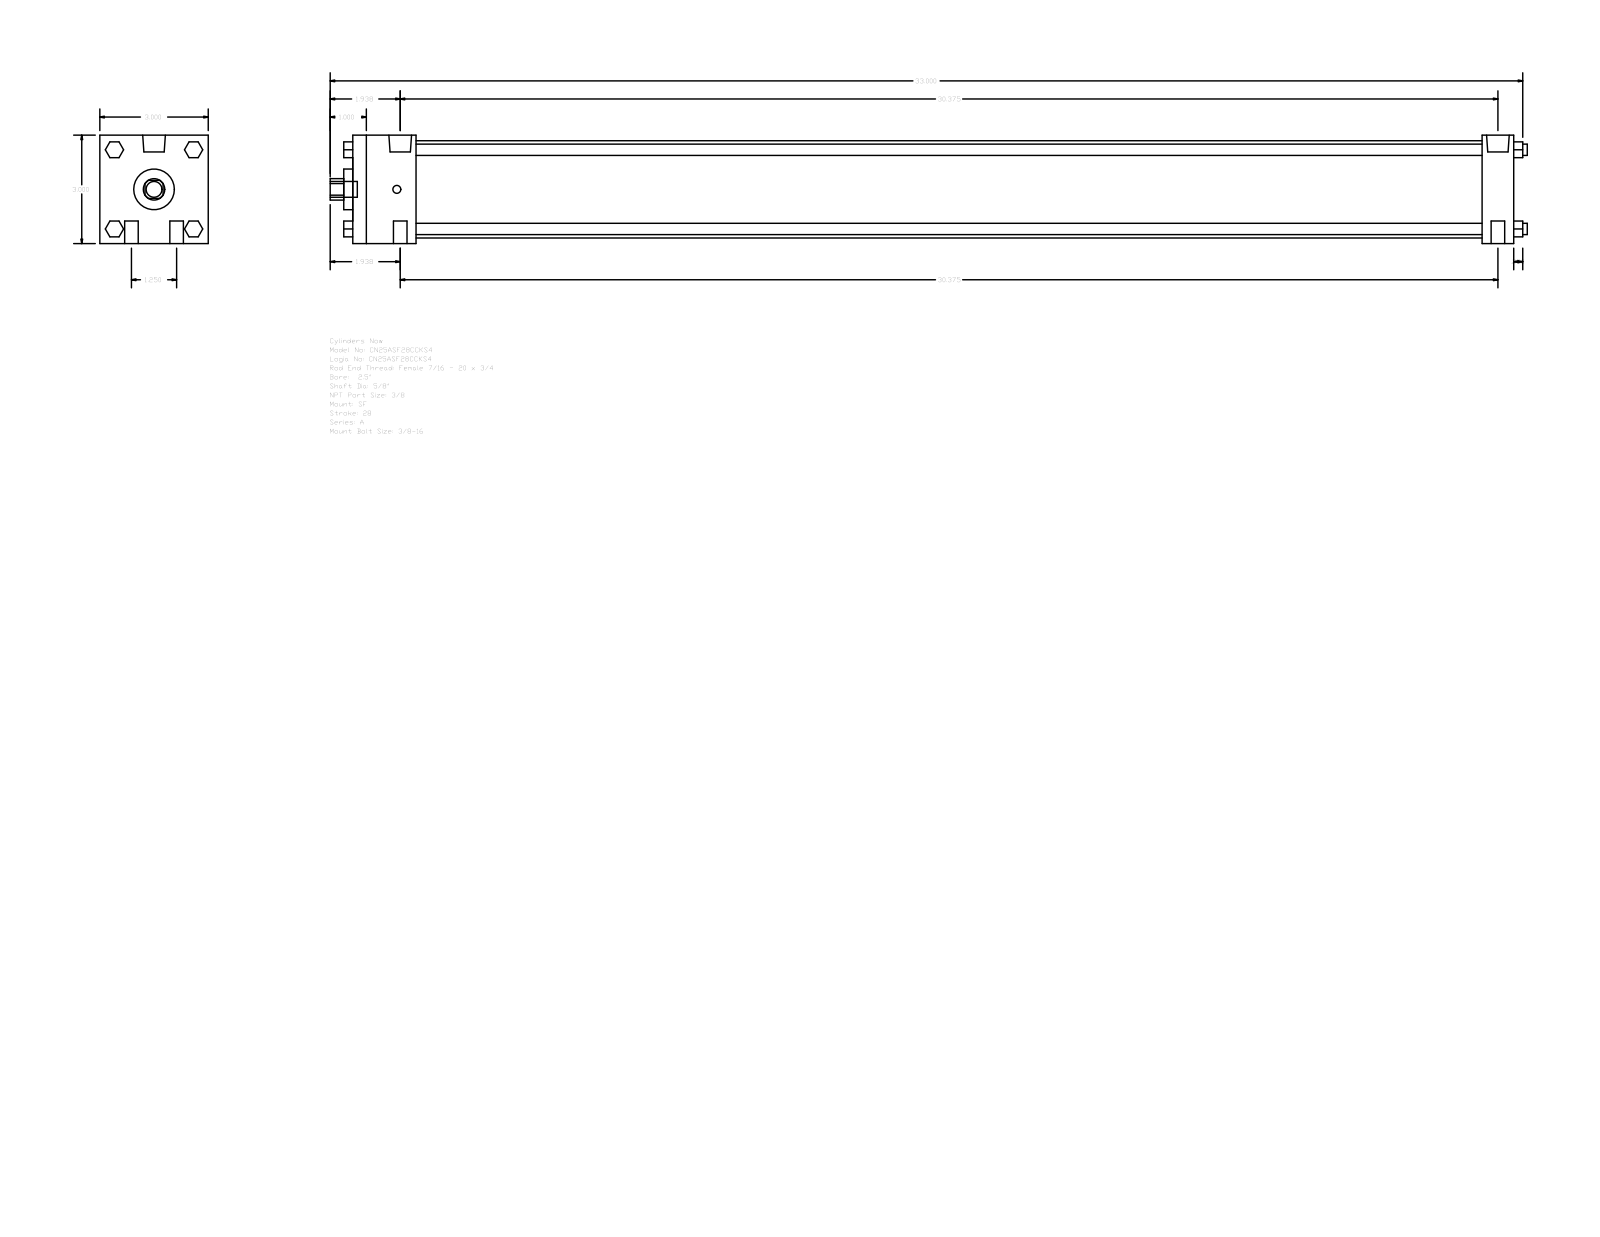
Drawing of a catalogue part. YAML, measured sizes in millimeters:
part_name: "A_SF__0250_0.625"
step_written_by: "GSSL Pune (CONFIG_CONTROL_DESIGN)"
units: millimeters
bodies: {solids: 0, faces: 124, planar: 94, cylindrical: 30, other: 0}
overall_size: [841.38, 76.2, 76.2]
round_holes:
  - {diameter: 15.88, count: 1}
  - {diameter: 28.57, count: 1}
  - {diameter: 68.33, count: 1}
round_bosses_or_shafts:
  - {diameter: 9.53, count: 4}
  - {diameter: 7.94, count: 4}
  - {diameter: 15.93, count: 2}
  - {diameter: 5.56, count: 2}
  - {diameter: 11.11, count: 1}
partial_cylinders:
  - {radius: 7.54, count: 1}
face_to_face_distances: [76.2, 815.97, 44.45, 793.74, 22.23, 749.29, 771.52, 6.35, 822.32, 50.8]
